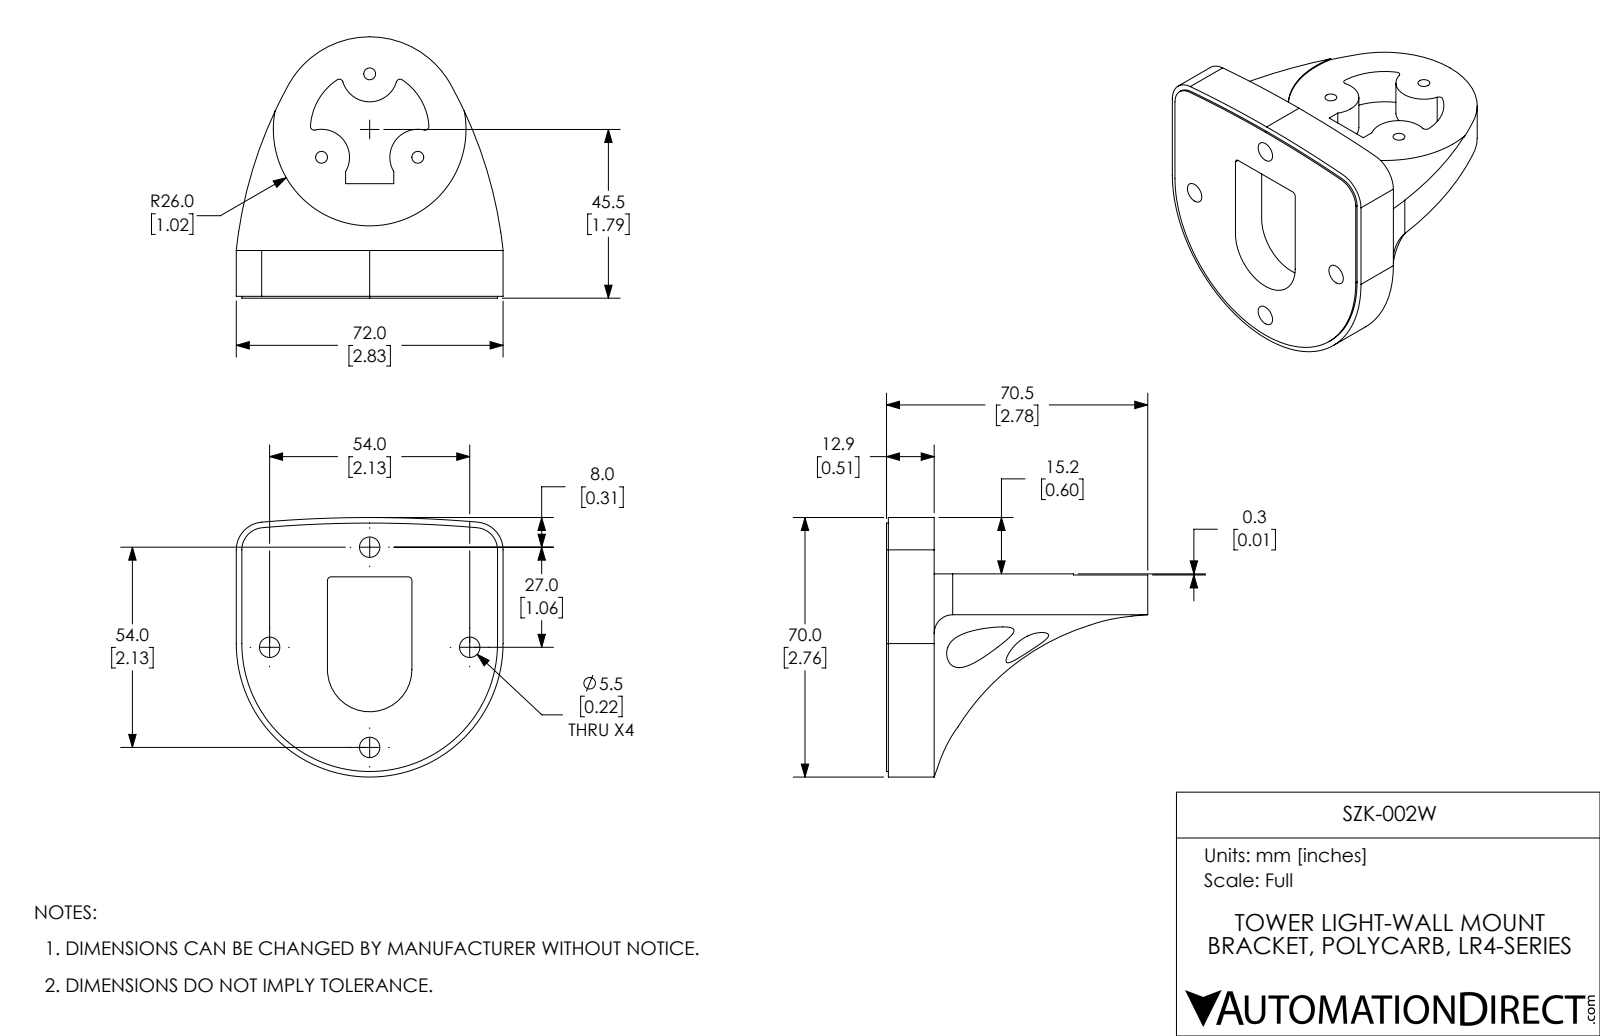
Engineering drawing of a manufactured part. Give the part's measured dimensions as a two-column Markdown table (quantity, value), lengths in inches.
| quantity | value |
| --- | --- |
| part name | SZK-002W |
| STEP written by | SolidWorks 2017 (AUTOMOTIVE_DESIGN) |
| units | inches |
| bodies | 1 solid, 74 faces (21 planar, 41 cylindrical, 12 other) |
| overall size | 2.835 × 2.776 × 2.756 |
| volume | 6.088 in³ |
| surface area | 36.97 in² |
| round holes (diameter × count) | 0.217 × 4, 0.433 × 4, 0.126 × 3, 0.453 × 3 |
| partial cylindrical surfaces (radius × count) | 0.297 × 2, 4.599 × 2, 0.295 × 1, 1.024 × 1, 1.358 × 1, 1.417 × 1, 13.386 × 1 |
| main face-to-face distances | 0.394, 0.506, 0.113, 0.406, 0.487, 0.374, 0.02, 2.835, 0.276, 0.118 |
| hole center spacings | 1.503, 1.023, 2.126 |
